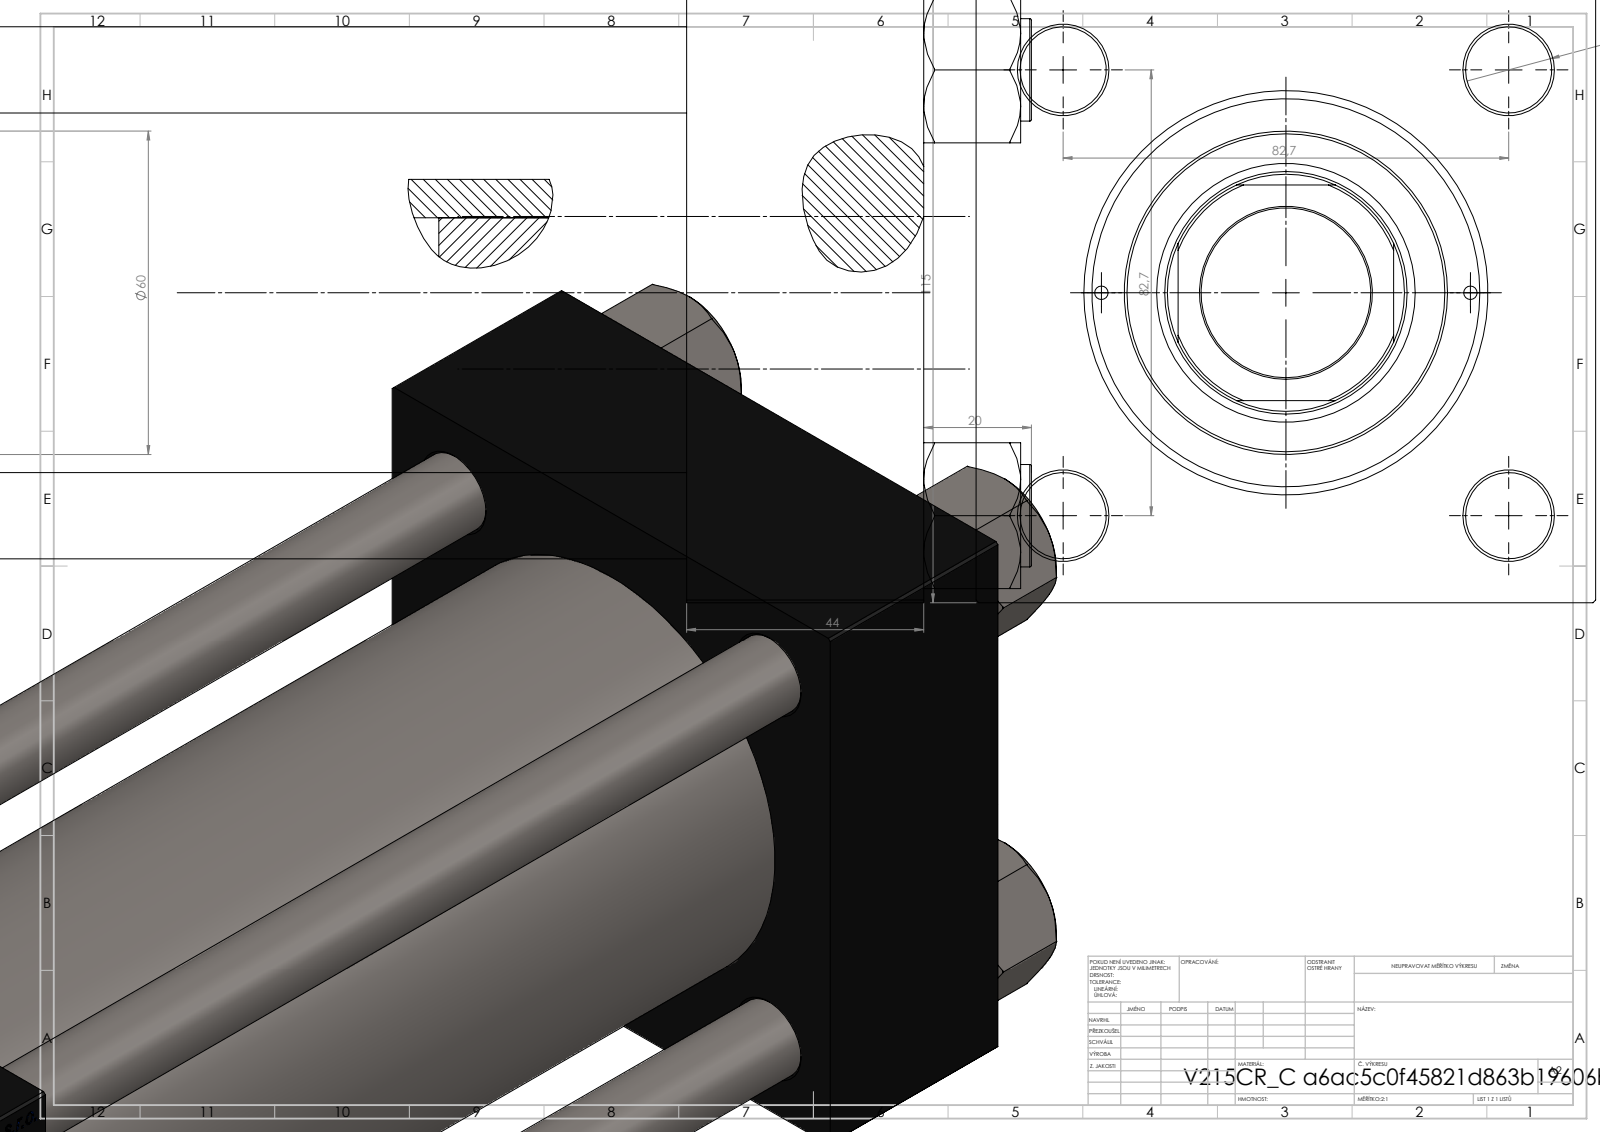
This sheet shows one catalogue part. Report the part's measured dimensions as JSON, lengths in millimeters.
{"part_name": "V215CR_C_Body; V215CR_C_TYCINKA; V215CR_VCP_C; V215_VC_A (+1 more)", "step_written_by": "SolidWorks 2019 (CONFIG_CONTROL_DESIGN)", "units": "millimeters", "bodies": {"solids": 11, "faces": 1202, "planar": 576, "cylindrical": 90, "other": 536}, "overall_size": [370, 115, 115], "volume_mm3": 2264000, "surface_area_mm2": 394906, "round_holes": [[16, 4], [2.5, 2], [7, 2], [26.44, 2], [35, 2], [31.5, 1], [45, 1], [48, 1], [61, 1], [72, 1], [80, 1]], "round_bosses_or_shafts": [[19, 4], [86, 1], [60, 1]], "partial_cylinders_radius": [[22, 1]], "face_to_face_distances": [115, 44, 319, 275, 250, 206, 69, 290.3, 246.3, 40.3], "hole_center_spacings": [41.96, 58.48, 82.7, 86.17, 34.25, 116.96, 68.5, 251]}
